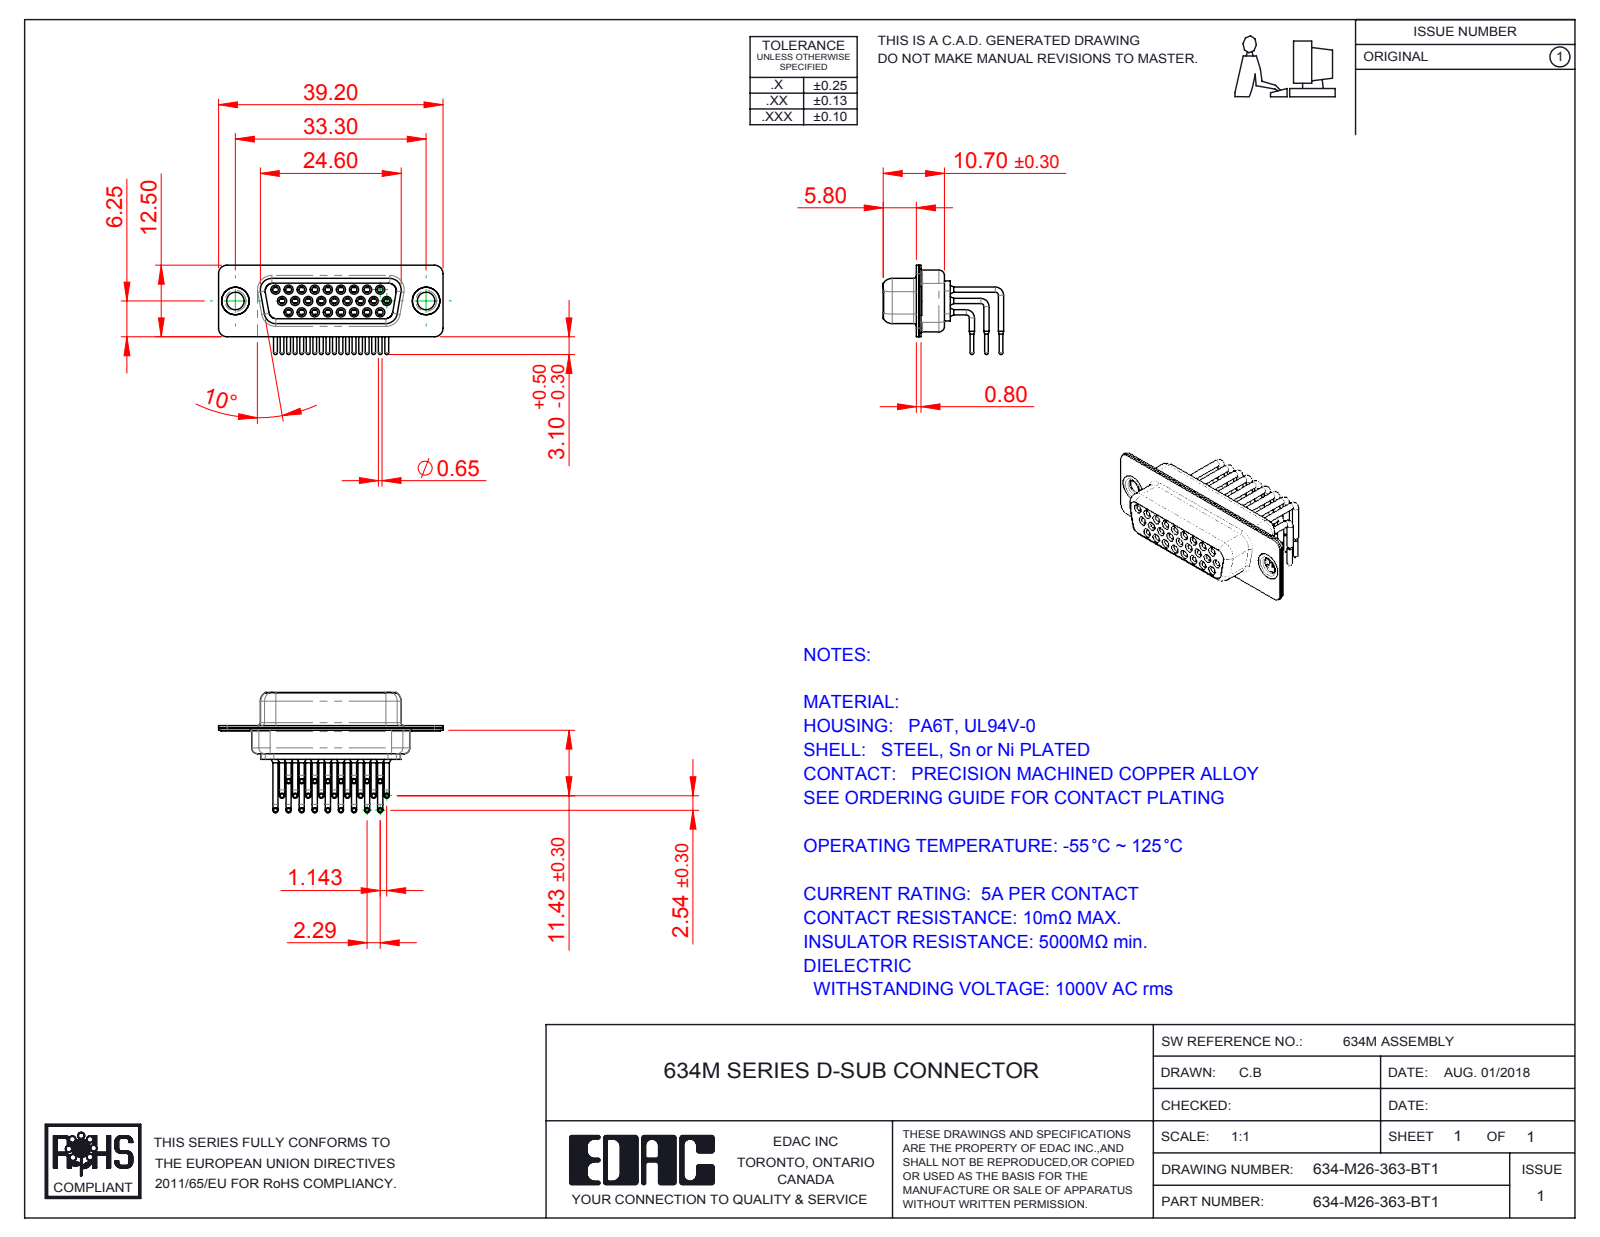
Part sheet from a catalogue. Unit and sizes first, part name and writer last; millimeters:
Units: millimetres
Overall size (bounding box): 39.2 × 21.02 × 15.6
Round holes (diameter × count): ⌀1 ×26, ⌀1.1 ×26, ⌀1.7 ×26, ⌀1.8 ×26, ⌀2 ×26, ⌀3.05 ×2, ⌀4 ×2, ⌀4.8 ×2
Round bosses / shafts (diameter × count): ⌀0.9 ×52, ⌀1.6 ×26, ⌀1.5 ×26, ⌀0.65 ×26, ⌀5 ×2, ⌀4.9 ×2, ⌀3.55 ×2, ⌀2 ×1
Partial cylindrical surfaces — rounded edges, fillets, slot ends (radius × count): R1.5 ×16, R2 ×12, R1.35 ×8, R1.6 ×8, R0.25 ×4, R0.5 ×4, R0.6 ×4, R0.65 ×4
Main face-to-face distances: 0.4, 1.45, 8.95, 8.5, 1.9, 2.3, 0.8, 6.2, 0.45, 7.05
Hole centre spacings: 3.96, 2.28, 4.57, 6.05, 2.29, 8.24, 6.86, 6.04
Volume: 2 454 mm³ · Surface area: 8 321 mm²
Bodies: 31 solids, 1631 faces (457 planar, 719 cylindrical, 455 other)
Part name (STEP PRODUCT): 634M Shell Rear_26 Contacts; 634M Shell Front_26 Contacts; 634M Housing_26 Contacts; 634-M26-363-BT1 (+4 more)
STEP written by: SolidWorks 2016 (CONFIG_CONTROL_DESIGN)
